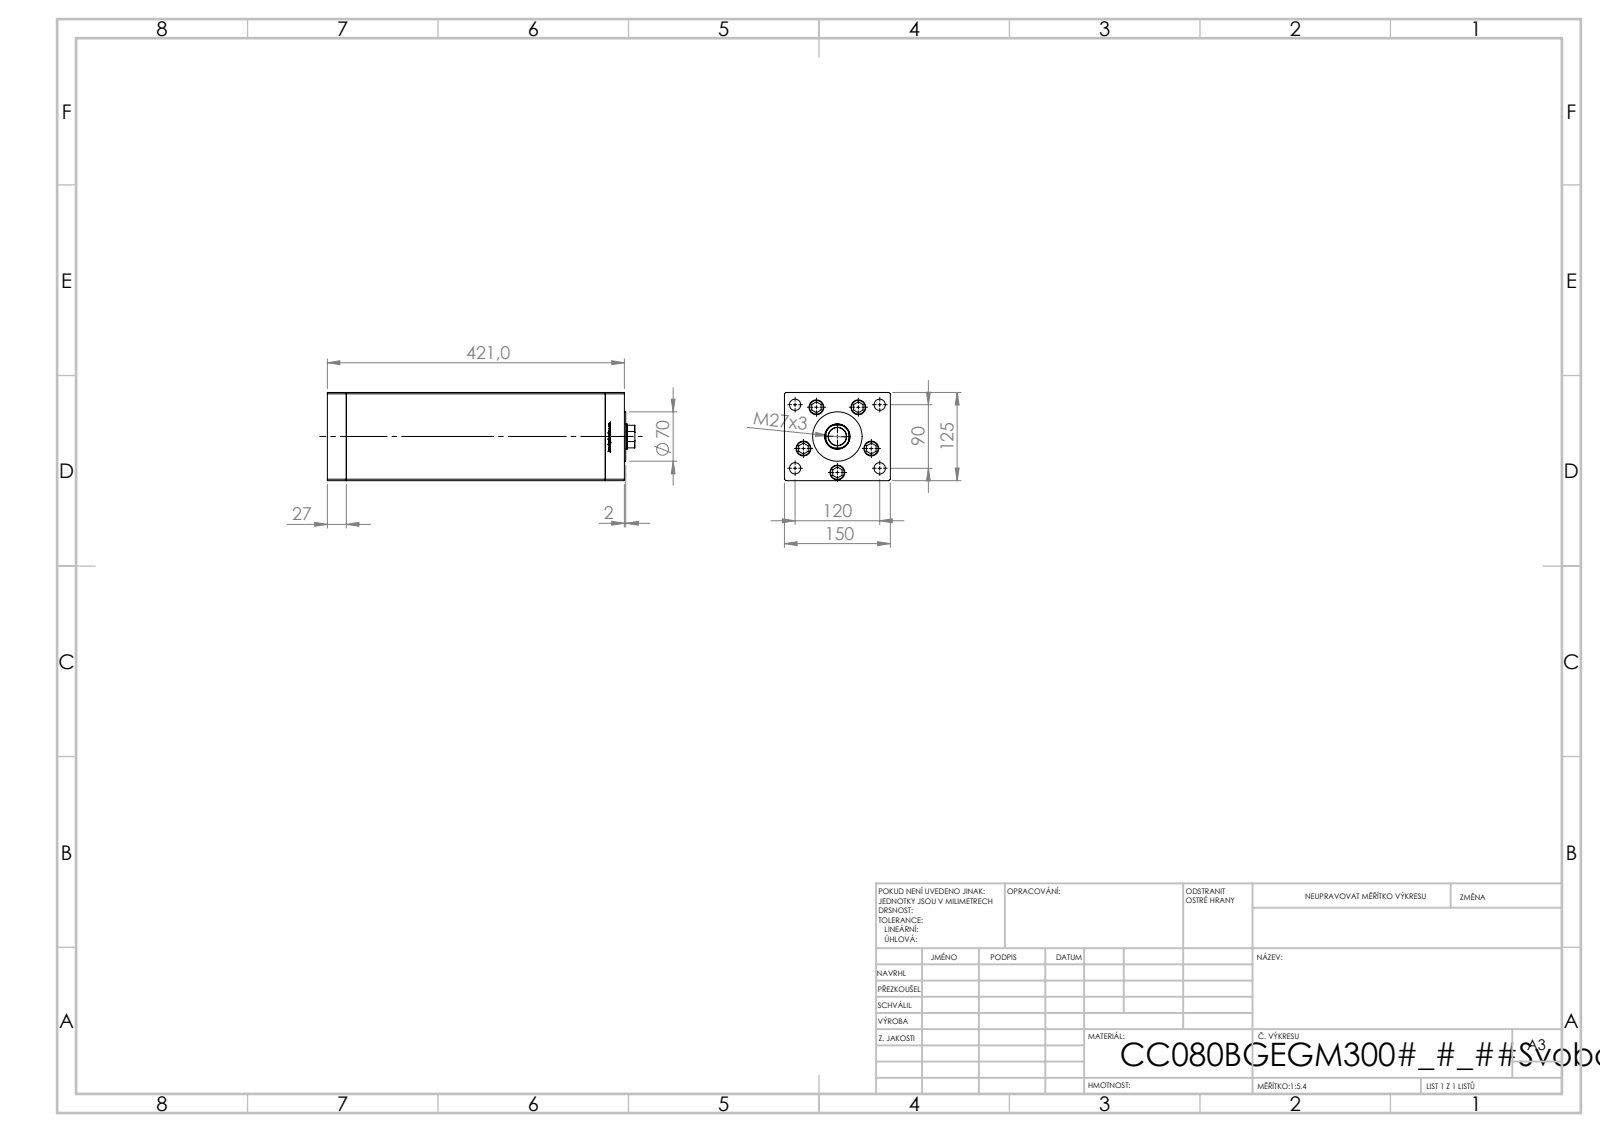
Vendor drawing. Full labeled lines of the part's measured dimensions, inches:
Part name (STEP PRODUCT): V220C_B MIDDLE; V220C_VC_B; V220C_FRONT_B; V220C BACK_B (+1 more)
STEP written by: SolidWorks 2019 (CONFIG_CONTROL_DESIGN)
Units: inches
Bodies: 14 solids, 1185 faces (464 planar, 147 cylindrical, 574 other)
Overall size (bounding box): 17.165 × 5.906 × 4.921
Volume: 395.9 in³ · Surface area: 859.7 in²
Round holes (diameter × count): ⌀0.689 ×5, ⌀0.827 ×5, ⌀0.63 ×4, ⌀0.079 ×2, ⌀0.518 ×2, ⌀1.004 ×1, ⌀1.417 ×1
Round bosses / shafts (diameter × count): ⌀0.315 ×5, ⌀3.15 ×1, ⌀2.756 ×1
Partial cylindrical surfaces — rounded edges, fillets, slot ends (radius × count): R0.037 ×2, R0.689 ×1
Main face-to-face distances: 4.921, 5.906, 1.063, 15.512, 14.449, 1.319, 0.256, 16.575, 14.193, 15.256
Hole centre spacings: 2.008, 2.953, 1.198, 1.2, 2.319, 2.374, 2.411, 2.486
